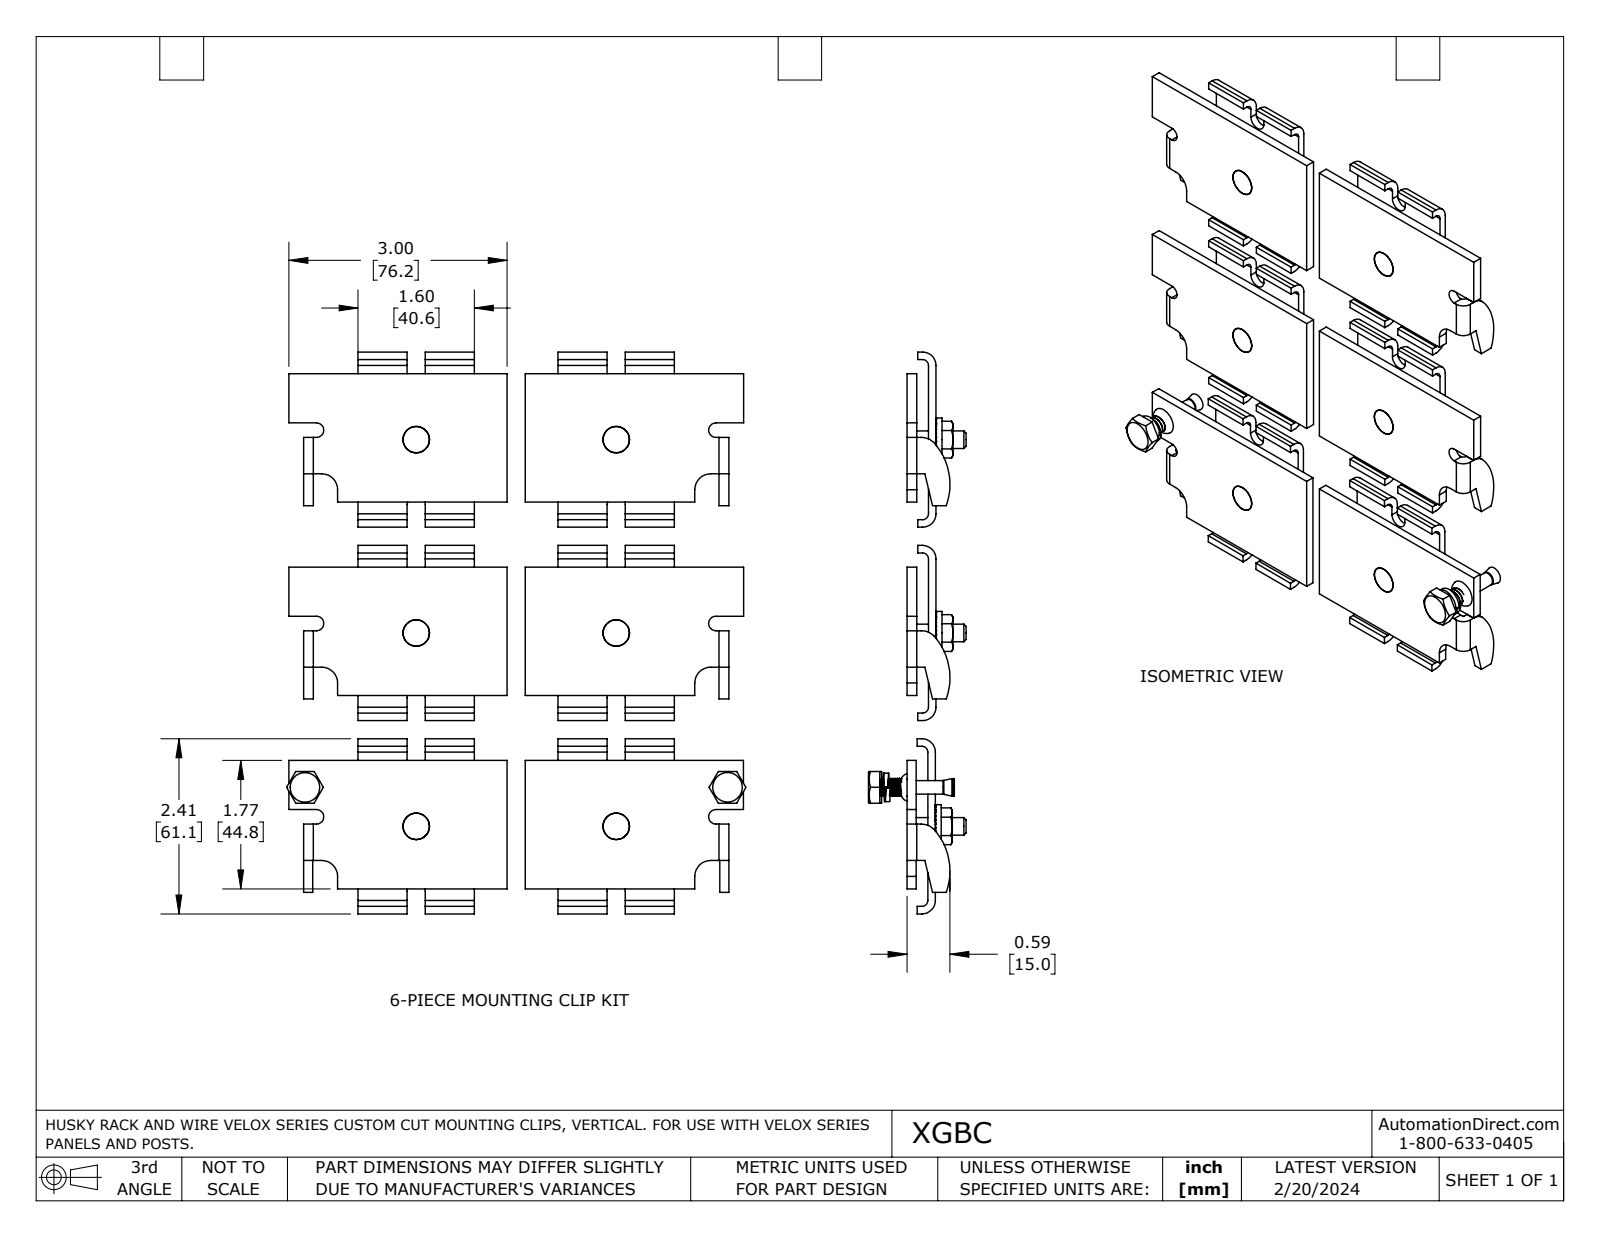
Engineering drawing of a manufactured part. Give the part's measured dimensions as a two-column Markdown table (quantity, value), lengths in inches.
| quantity | value |
| --- | --- |
| part name | XGBC_Default |
| STEP written by | SolidWorks 2023 (CONFIG_CONTROL_DESIGN) |
| units | inches |
| bodies | 28 solids, 970 faces (690 planar, 168 cylindrical, 112 other) |
| overall size | 7.721 × 6.315 × 1.344 |
| volume | 6.899 in³ |
| surface area | 137.6 in² |
| round holes (diameter × count) | 0.25 × 8, 0.185 × 6, 0.253 × 4, 0.201 × 2, 0.228 × 2 |
| round bosses / shafts (diameter × count) | 0.594 × 6, 0.43 × 6, 0.243 × 6, 0.39 × 2, 0.187 × 2 |
| partial cylindrical surfaces (radius × count) | 0.125 × 12, 0.137 × 12, 0.08 × 6, 0.1 × 6, 0.184 × 6, 0.218 × 6, 0.25 × 3, 0.865 × 3 |
| main face-to-face distances | 0.134, 0.104, 0.264, 0.16, 0.398, 0.294, 0.125, 0.273, 0.169, 0.094 |
| hole center spacings | 2.75, 2.657, 2.657, 3.824, 3.824, 4.777, 5.017, 5.314 |
